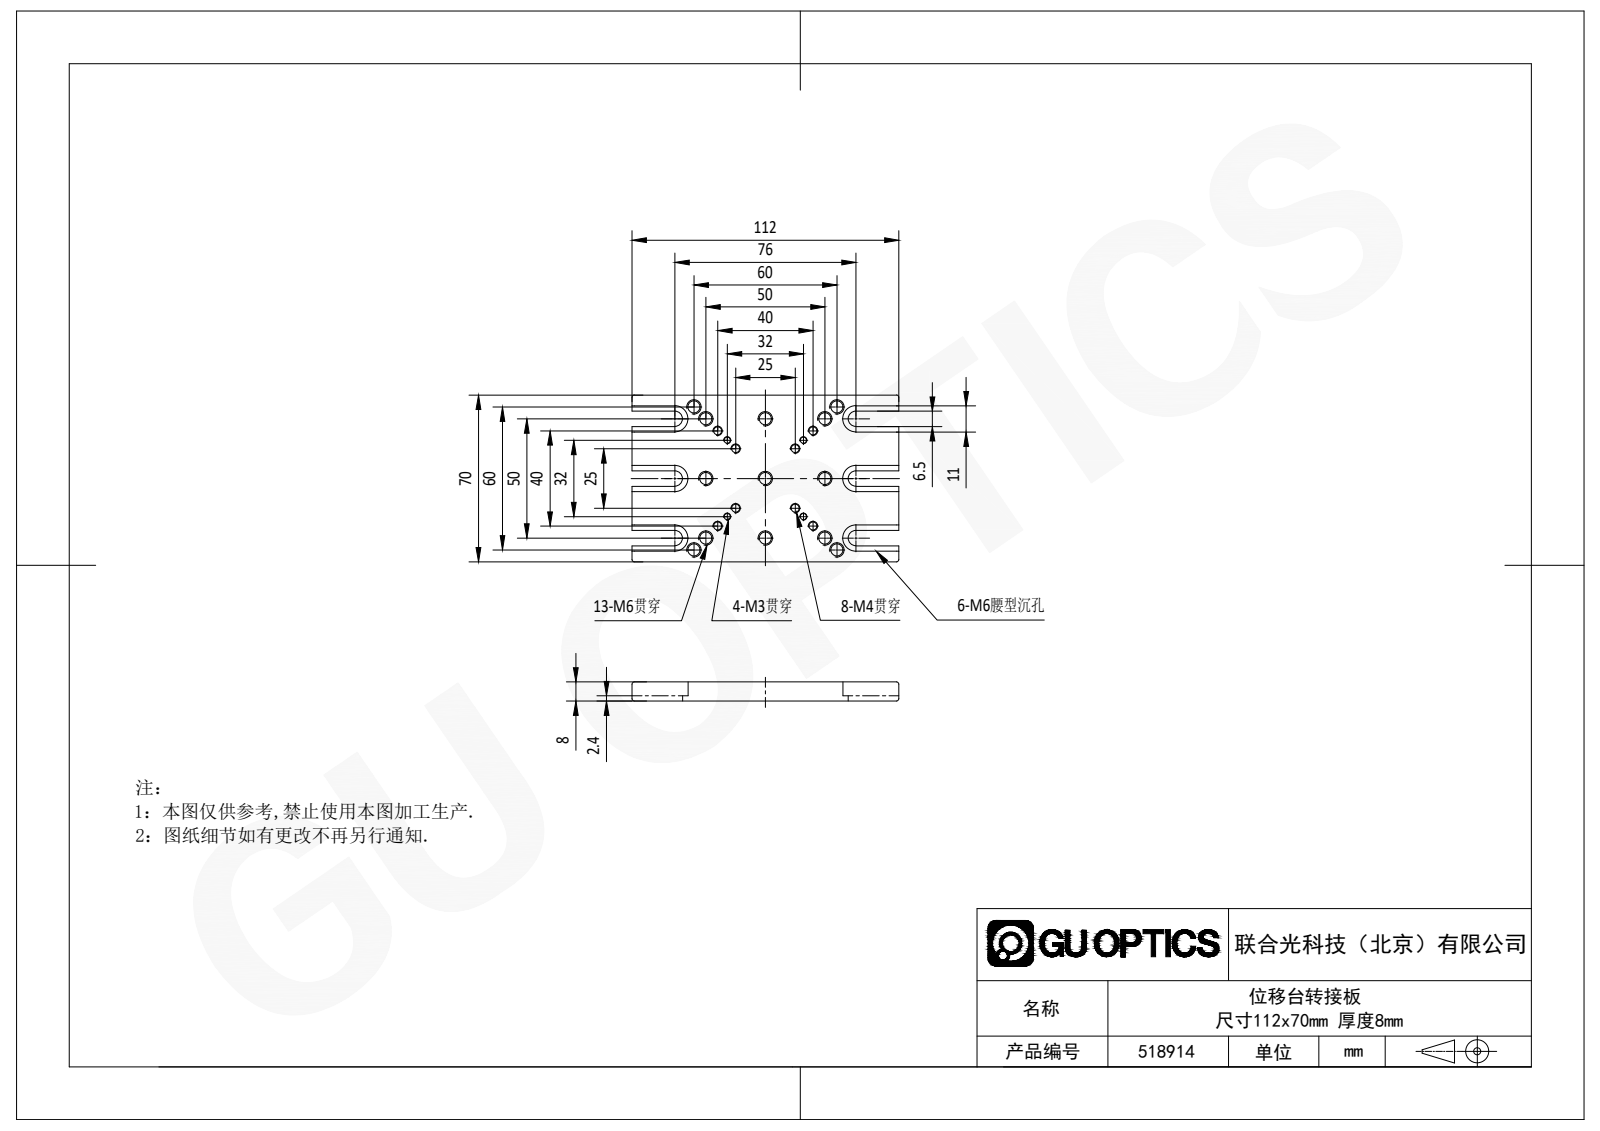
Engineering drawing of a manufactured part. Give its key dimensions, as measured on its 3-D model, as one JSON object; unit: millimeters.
{"step_written_by": "SolidWorks 2020 (CONFIG_CONTROL_DESIGN)", "units": "millimeters", "bodies": {"solids": 1, "faces": 136, "planar": 42, "cylindrical": 61, "other": 33}, "overall_size": [112, 70, 8], "volume_mm3": 49624, "surface_area_mm2": 20476, "round_holes": [[5, 13], [3.3, 8], [2.5, 4]], "partial_cylinders_radius": [[1, 12], [3.25, 6], [5.5, 6]], "face_to_face_distances": [8, 25, 2.4, 5.6, 70, 11, 50, 2.25, 8.75, 4.5], "hole_center_spacings": [17.68, 25, 39.53, 45.96, 35.36, 7.07, 18.36, 20.62]}
